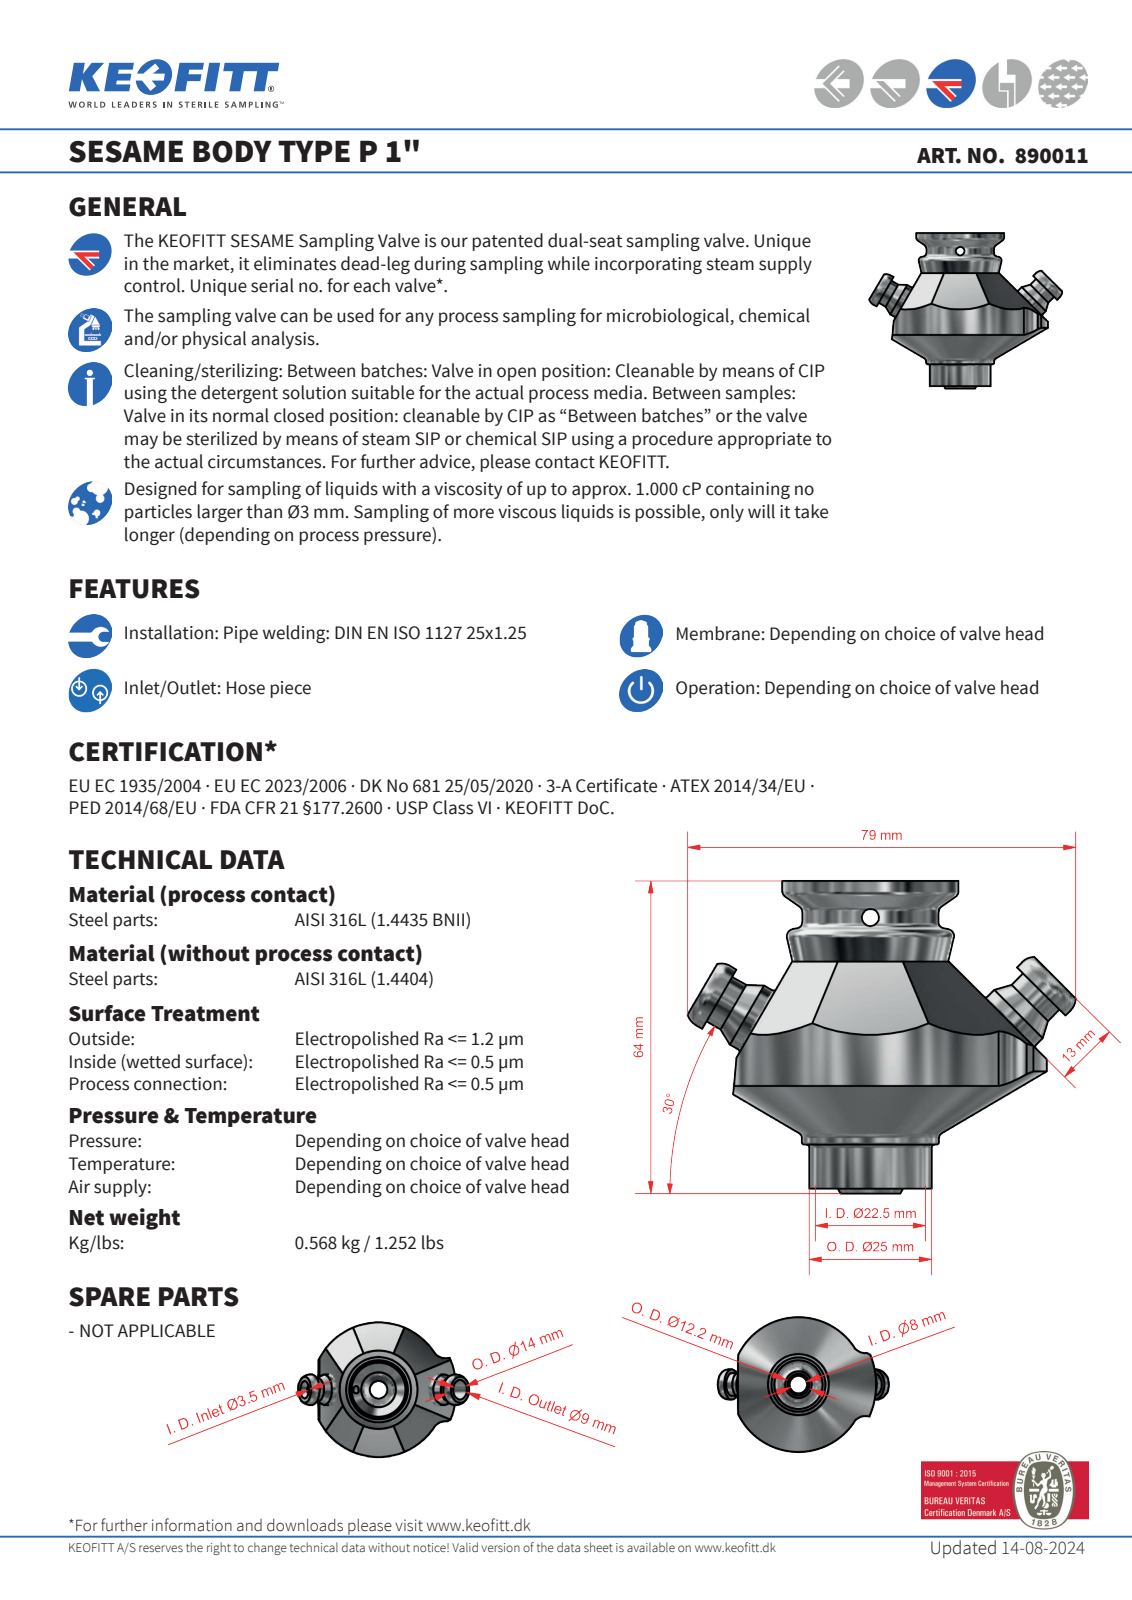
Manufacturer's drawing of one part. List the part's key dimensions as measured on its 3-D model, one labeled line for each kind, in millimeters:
Part name (STEP PRODUCT): 890011
STEP written by: Autodesk Inventor 2017 (AUTOMOTIVE_DESIGN)
Units: millimetres
Bodies: 1 solid, 98 faces (26 planar, 41 cylindrical, 31 other)
Overall size (bounding box): 79.23 × 64 × 62
Volume: 90 940 mm³ · Surface area: 17 589 mm²
Round holes (diameter × count): ⌀3.5 ×3, ⌀8 ×1, ⌀9 ×1, ⌀16 ×1, ⌀22.5 ×1, ⌀29 ×1, ⌀30 ×1
Round bosses / shafts (diameter × count): ⌀14 ×2, ⌀10.5 ×2, ⌀36 ×1, ⌀28.7 ×1, ⌀28.5 ×1, ⌀28 ×1, ⌀26 ×1, ⌀25 ×1
Partial cylindrical surfaces — rounded edges, fillets, slot ends (radius × count): R7 ×2, R31 ×1, R36 ×1
Main face-to-face distances: 4.63, 3, 1.63, 17.87, 19.5, 22.5, 6, 11.87, 13.5, 16.5
